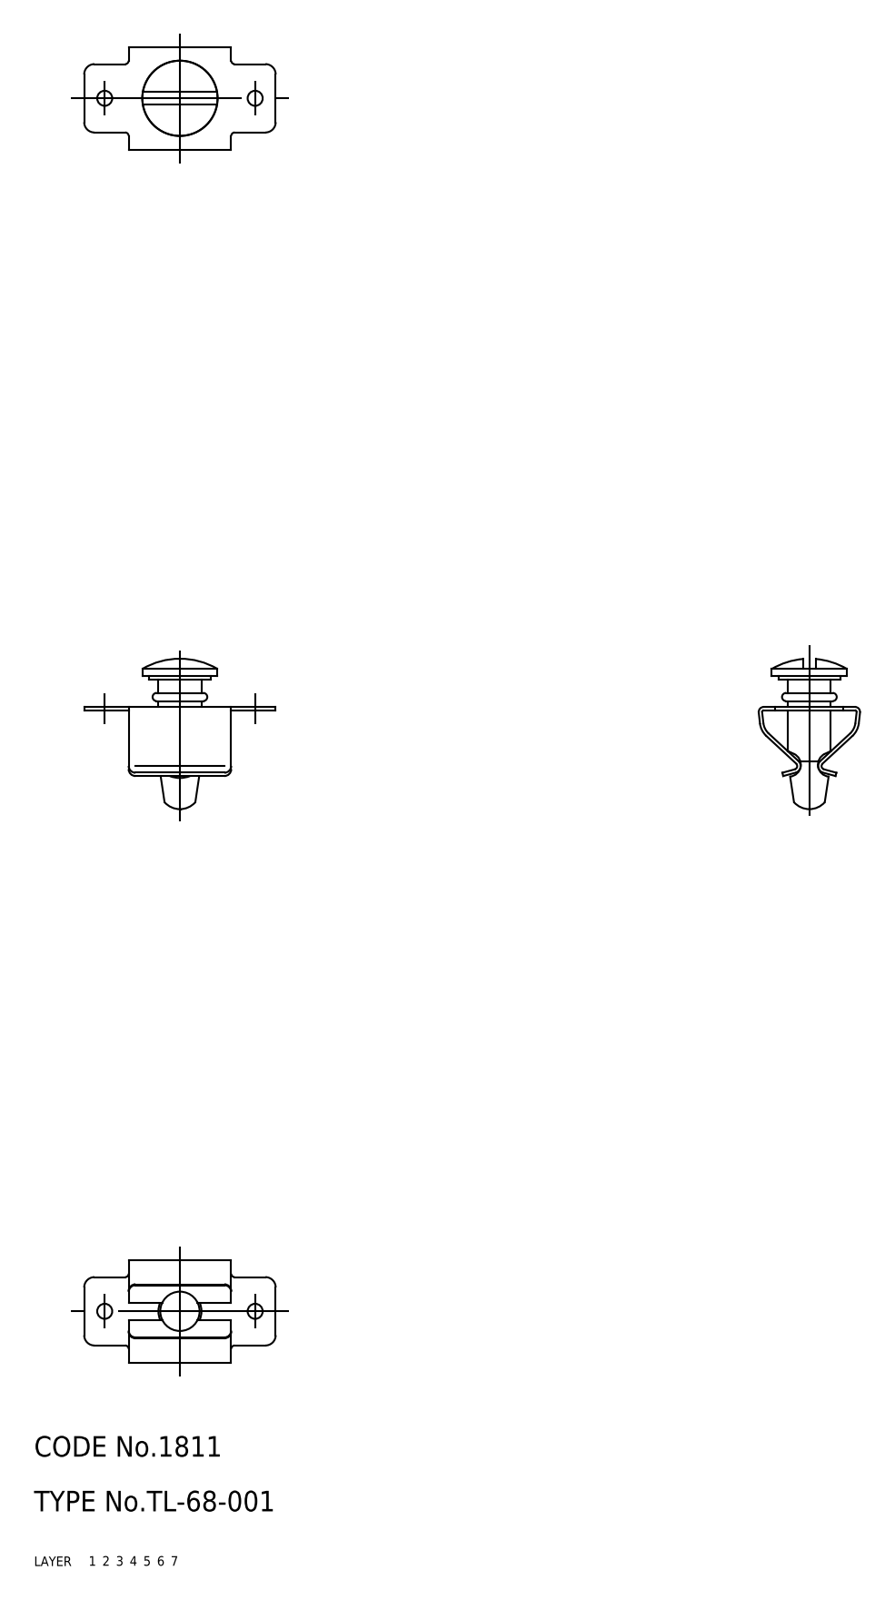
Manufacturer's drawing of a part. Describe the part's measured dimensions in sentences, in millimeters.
The part is named "leaf spring; fastener; TL_68_001_20830_36". Its 3-D file was written by "CADfix (AUTOMOTIVE_DESIGN)". It is 2 solids with 84 faces: 0 planar, 0 cylindrical and 84 other. Overall it measures 28 by 21.96 by 15 millimeters. Its volume is 1 004 cubic millimeters and its surface area 2 044 square millimeters.
